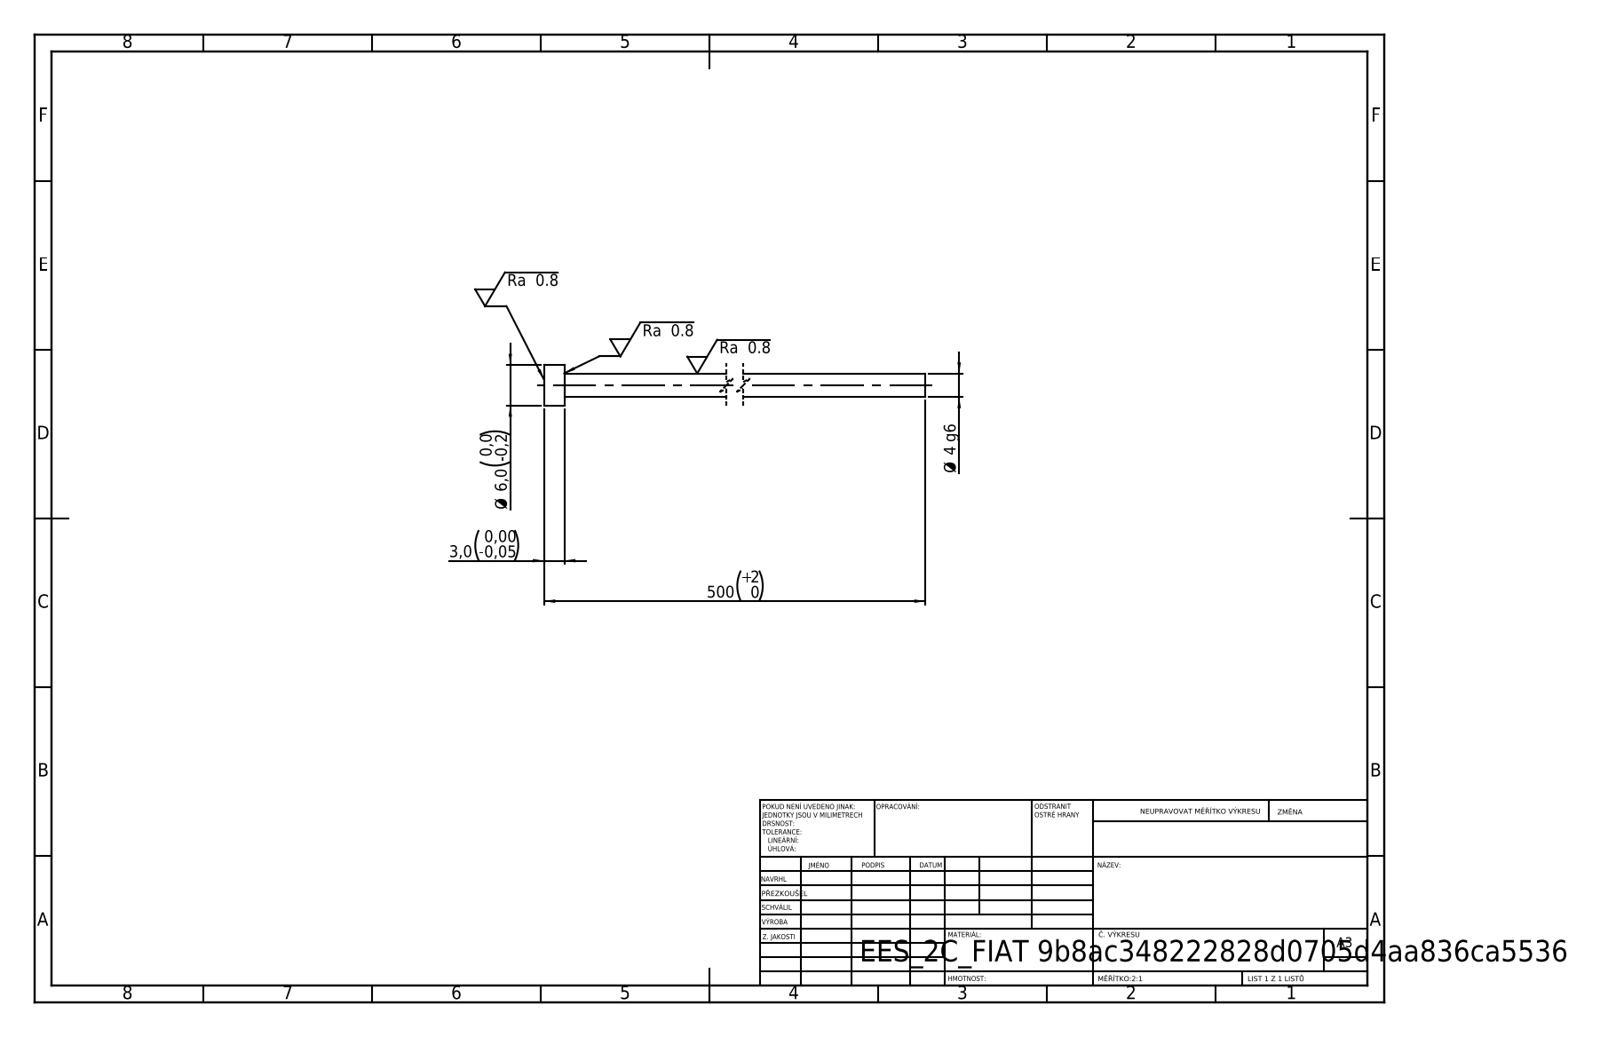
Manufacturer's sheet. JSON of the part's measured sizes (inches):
{"step_written_by": "SolidWorks 2019 (CONFIG_CONTROL_DESIGN)", "units": "inches", "bodies": {"solids": 1, "faces": 7, "planar": 3, "cylindrical": 4, "other": 0}, "overall_size": [19.685, 0.236, 0.236], "volume_in3": 0.297, "surface_area_in2": 8.646, "round_bosses_or_shafts": [[0.236, 1], [0.138, 1]], "face_to_face_distances": [0.118, 19.685, 19.567]}
